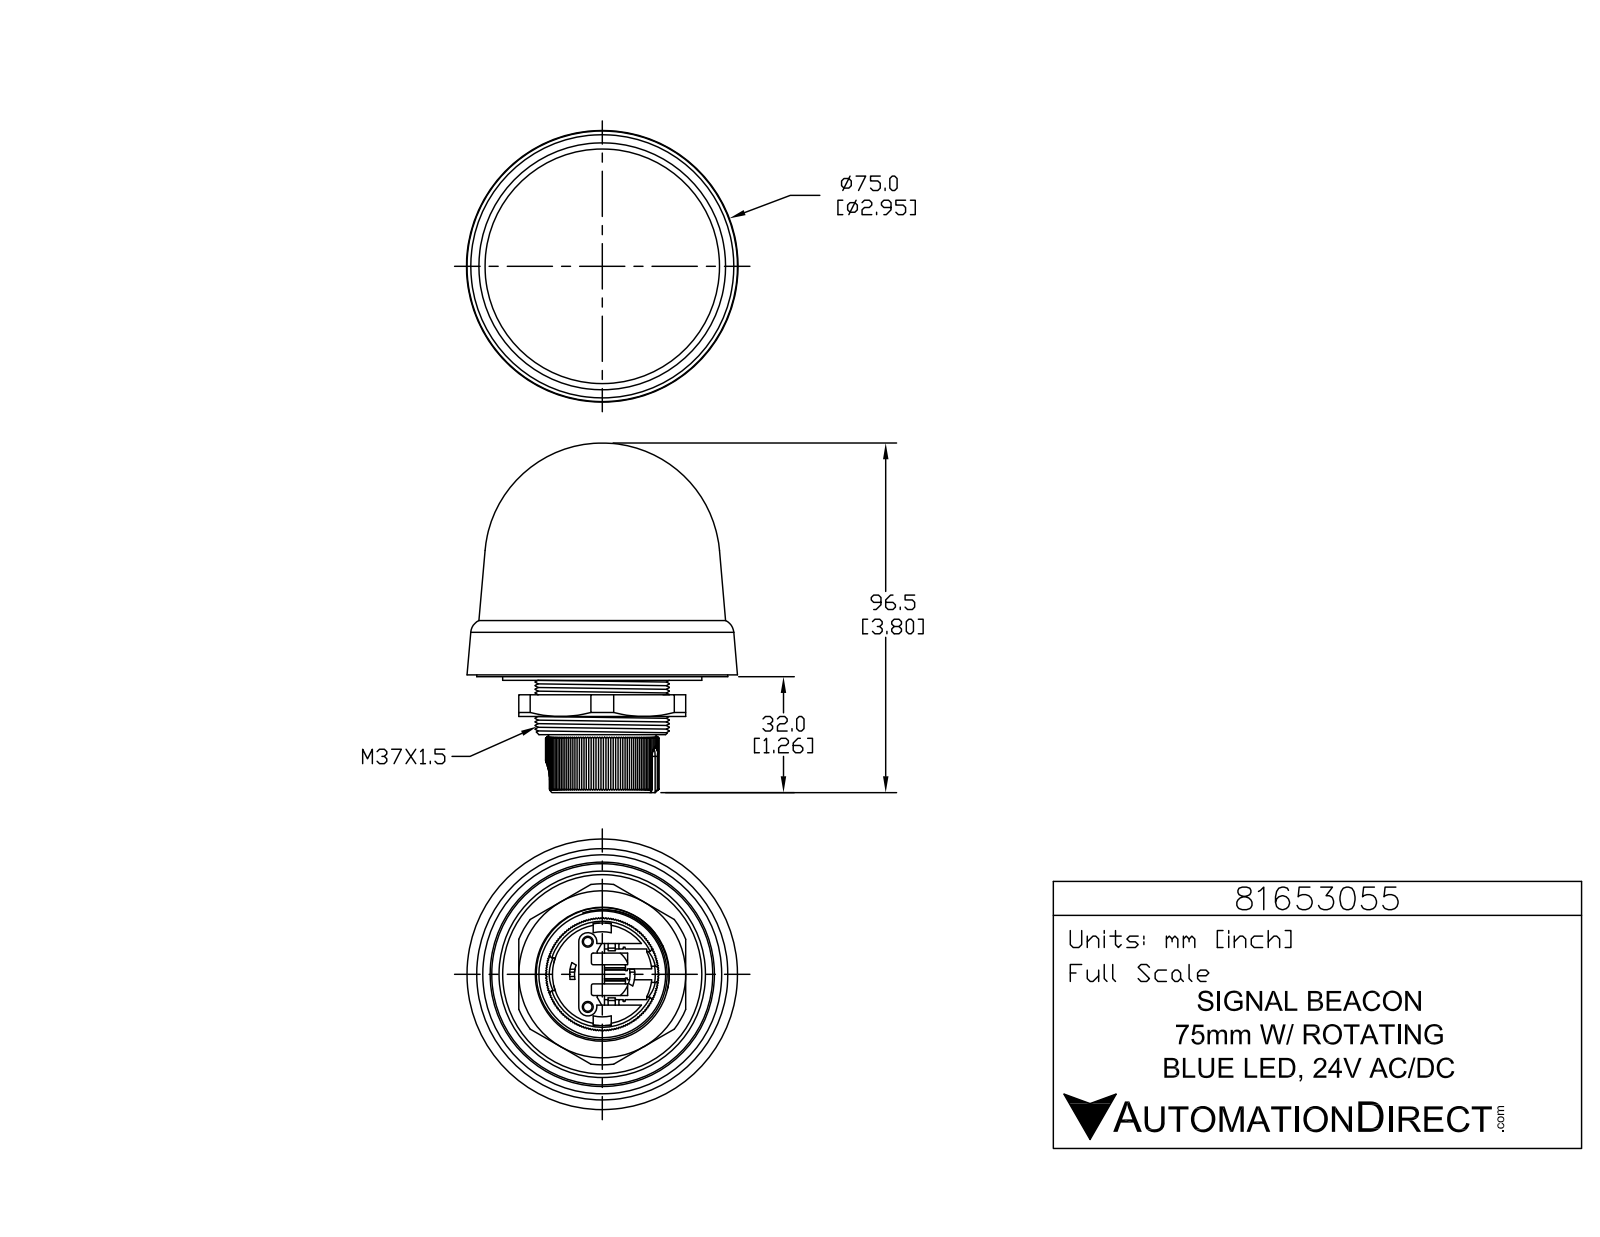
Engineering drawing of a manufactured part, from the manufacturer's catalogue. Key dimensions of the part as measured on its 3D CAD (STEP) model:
Part name (STEP PRODUCT): 81653055
STEP written by: SolidWorks 2019 (CONFIG_CONTROL_DESIGN)
Units: inches
Bodies: 3 solids, 560 faces (432 planar, 80 cylindrical, 48 other)
Overall size (bounding box): 3.799 × 2.941 × 2.941
Volume: 12.36 in³ · Surface area: 58.68 in²
Round holes (diameter × count): ⌀0.094 ×2, ⌀0.118 ×2, ⌀0.604 ×1, ⌀1.142 ×1
Round bosses / shafts (diameter × count): ⌀0.217 ×2, ⌀0.067 ×2, ⌀2.165 ×1, ⌀1.457 ×1, ⌀0.925 ×1
Partial cylindrical surfaces — rounded edges, fillets, slot ends (radius × count): R0.008 ×6, R0.039 ×6, R0.02 ×4, R0.031 ×2, R0.079 ×2, R0.098 ×2, R0.177 ×1, R0.354 ×1
Main face-to-face distances: 0.177, 0.354, 0.197, 0.433, 0.512, 0.335, 0.059, 0.394, 0.118, 0.157
Hole centre spacings: 0.388, 0.709
